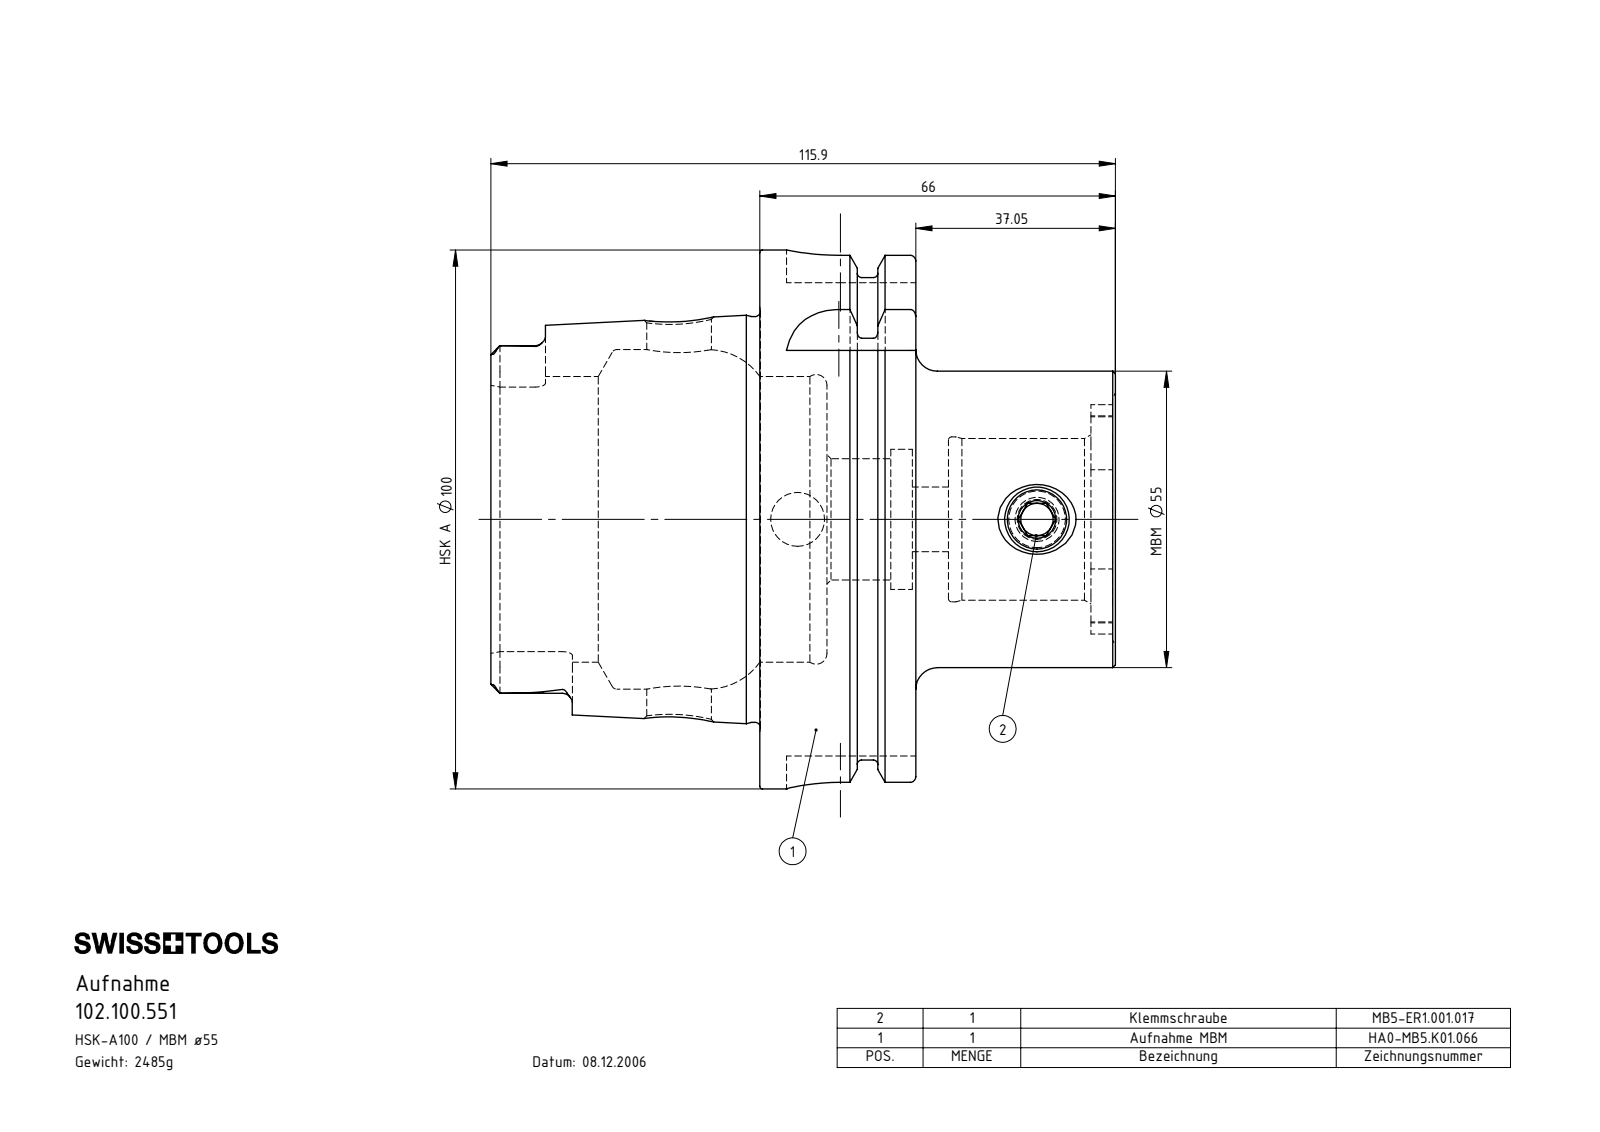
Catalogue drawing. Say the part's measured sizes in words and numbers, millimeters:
The part is named "HA0.MB5.K01.066; MB5-ER1.001.017_A; HA0-MB5.K01.066_A_Fertigbearbeitung". Its 3-D file was written by "SolidWorks 2011 (CONFIG_CONTROL_DESIGN)". It is 2 solids with 210 faces: 58 planar, 65 cylindrical and 87 other. Overall it measures 115.9 by 100 by 100 millimeters. Its volume is 316 598 cubic millimeters and its surface area 59 870 square millimeters. Round holes: 2 of diameter 12, 1 of diameter 10, 1 of diameter 11, 1 of diameter 22.5, 1 of diameter 26, 1 of diameter 30, 1 of diameter 30.6, 1 of diameter 53, 1 of diameter 63. Round bosses or shafts: 1 of diameter 100, 1 of diameter 91.95, 1 of diameter 75.26, 1 of diameter 55, 1 of diameter 12. Partial cylindrical surfaces (rounded edges, fillets, slot ends): 6 of radius 1.9, 4 of radius 4.88, 4 of radius 5.2, 4 of radius 10, 1 of radius 18.5, 1 of radius 21.27. The main face-to-face distances are 28.95, 16.5, 12.45, 49.9, 62.35, 78.85, 6.05, 35, 115.9, 66. The hole center spacings are 44.45.
